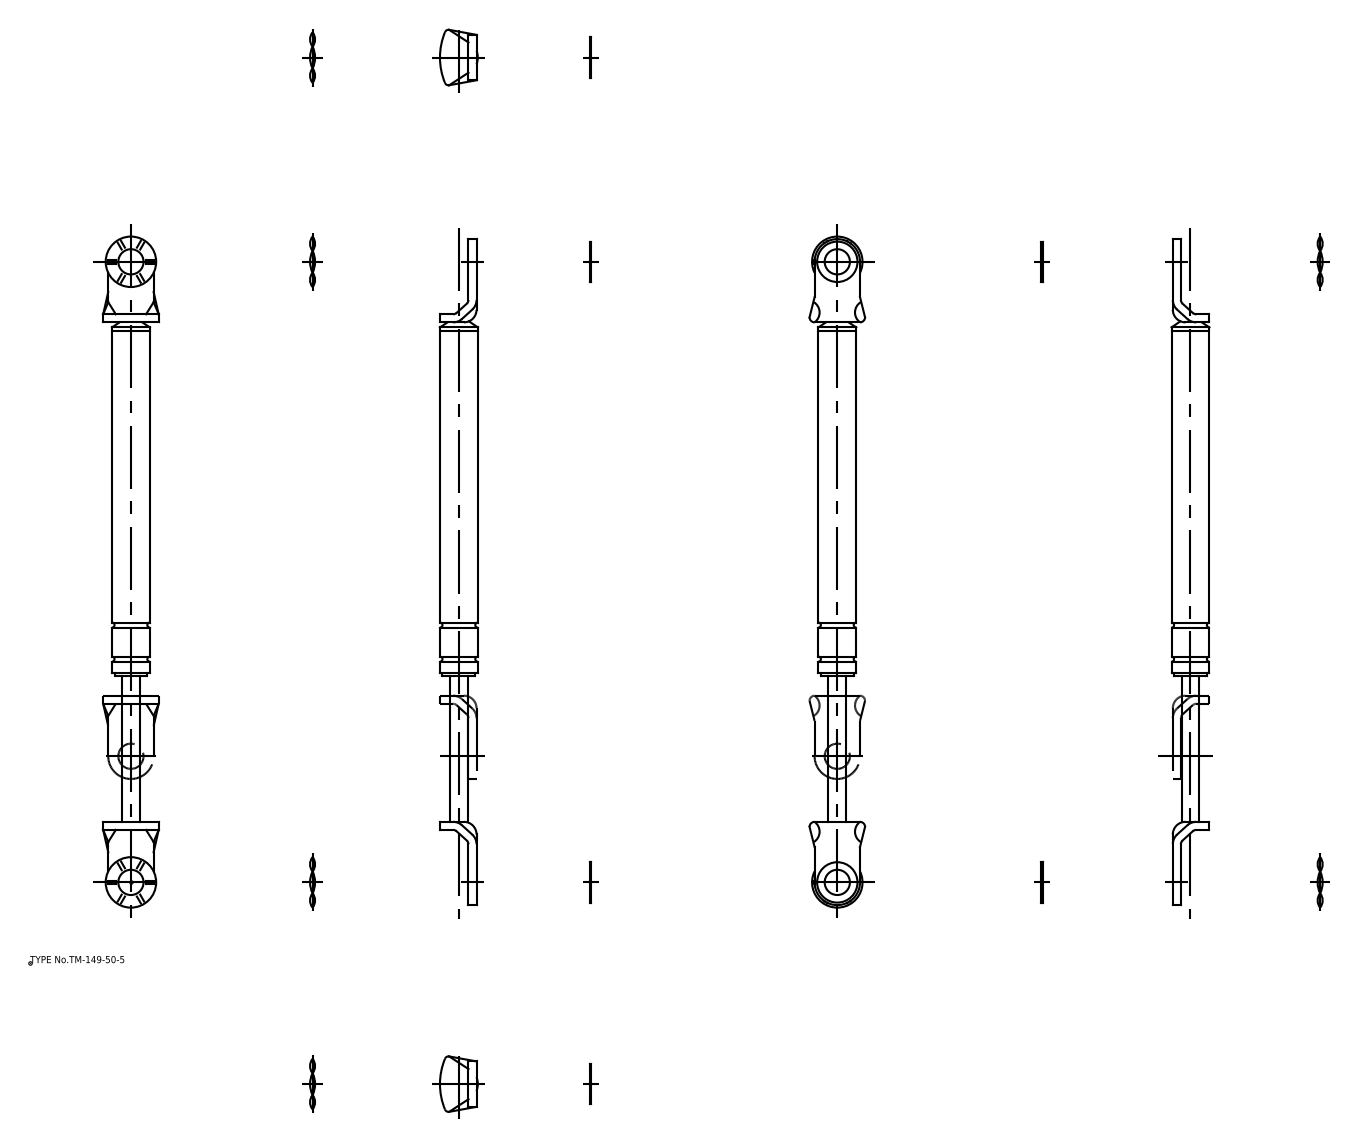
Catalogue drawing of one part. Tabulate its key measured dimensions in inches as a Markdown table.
| quantity | value |
| --- | --- |
| part name | washer_2; washer_1; body_div |
| STEP written by | spGate 16.7.1 (AUTOMOTIVE_DESIGN) |
| units | inches |
| bodies | 6 solids, 92 faces (44 planar, 42 cylindrical, 6 other) |
| overall size | 10.472 × 0.866 × 0.606 |
| volume | 1.969 in³ |
| surface area | 21.31 in² |
| round holes (diameter × count) | 0.394 × 2 |
| round bosses / shafts (diameter × count) | 0.787 × 2, 0.63 × 2, 0.606 × 1, 0.591 × 1, 0.512 × 1, 0.276 × 1 |
| partial cylindrical surfaces (radius × count) | 0.079 × 2, 0.197 × 2, 0.354 × 2, 0.674 × 1 |
| main face-to-face distances | 0.126, 0.079, 0.205, 7.921, 0.02, 0.146, 0.224, 8.047, 2.409, 5.638 |
| hole center spacings | 9.685 |
